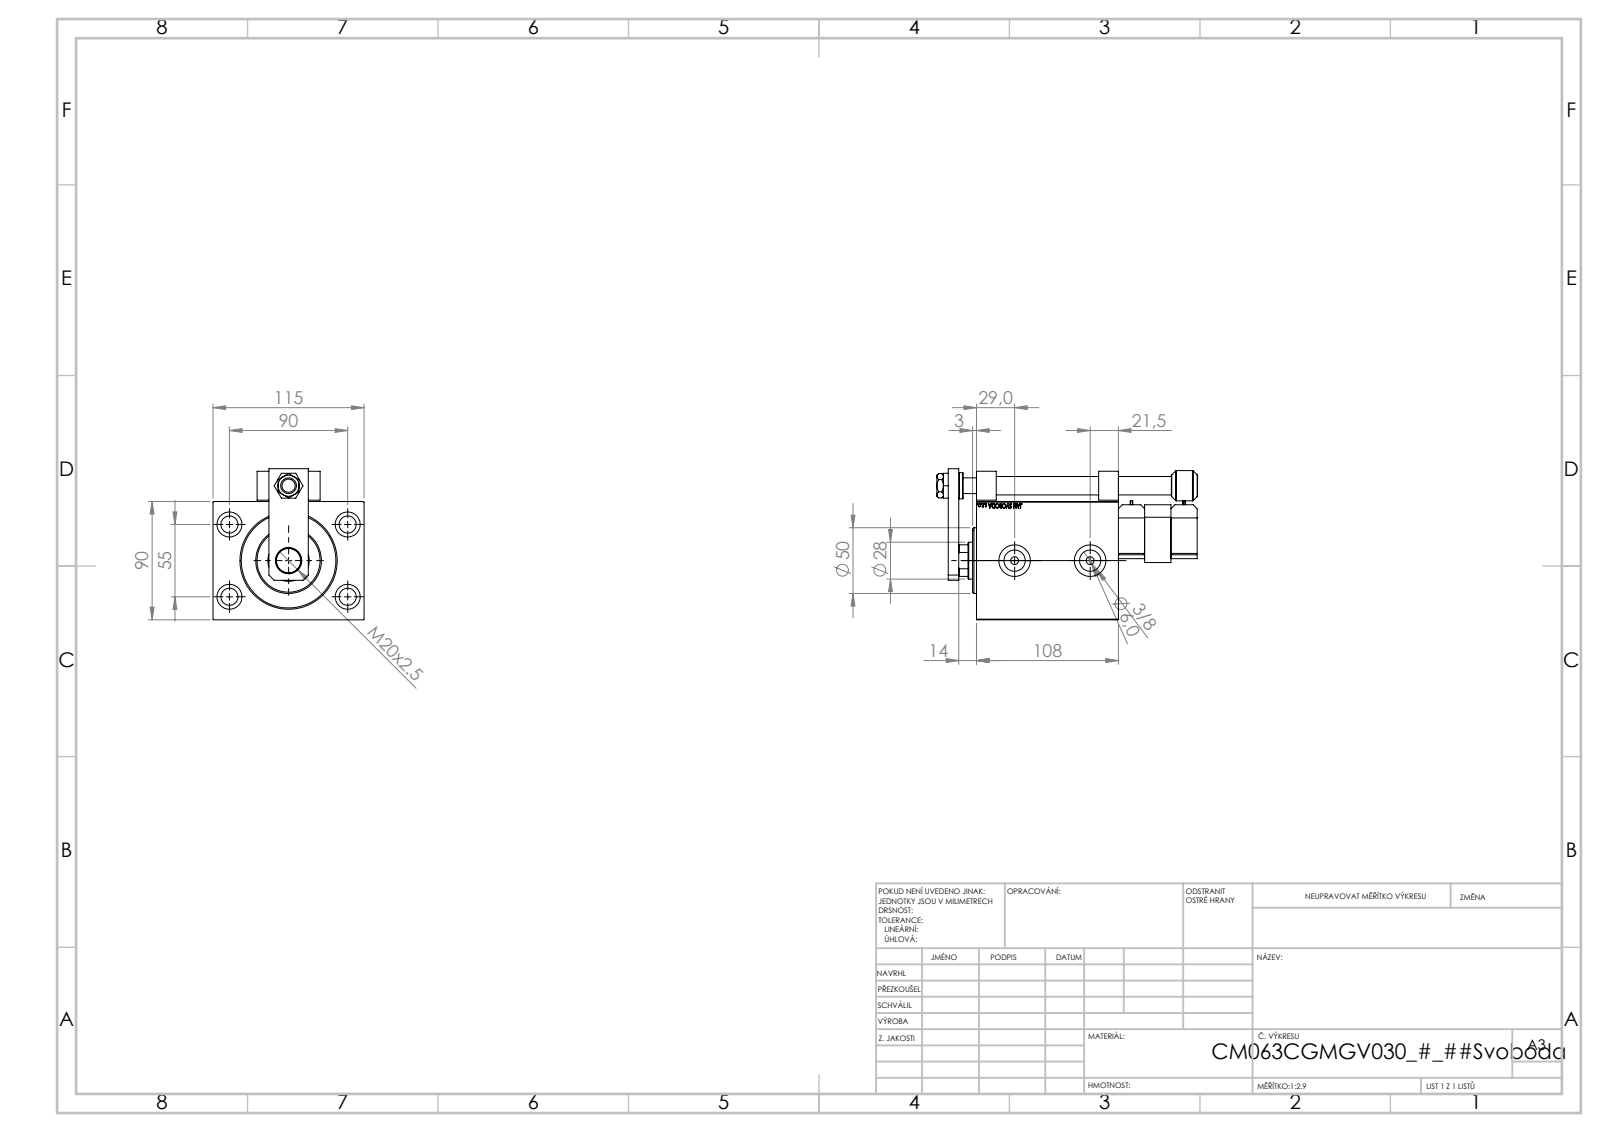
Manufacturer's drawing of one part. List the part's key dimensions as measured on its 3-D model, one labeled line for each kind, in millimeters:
Part name (STEP PRODUCT): MIDDLE; KROUZEK_PRO_TYC; V450CM_VC_B; SWITCH_P_FRONT_BACK (+7 more)
STEP written by: SolidWorks 2019 (CONFIG_CONTROL_DESIGN)
Units: millimetres
Bodies: 14 solids, 1090 faces (521 planar, 120 cylindrical, 449 other)
Overall size (bounding box): 198.5 × 115 × 115
Volume: 1 143 000 mm³ · Surface area: 187 436 mm²
Round holes (diameter × count): ⌀13 ×5, ⌀4 ×4, ⌀8 ×4, ⌀19 ×4, ⌀6 ×2, ⌀16.17 ×2, ⌀24 ×2, ⌀12 ×1, ⌀14 ×1, ⌀18.5 ×1, ⌀20 ×1, ⌀28 ×1
Round bosses / shafts (diameter × count): ⌀20 ×3, ⌀16 ×2, ⌀14 ×2, ⌀6 ×2, ⌀50 ×1, ⌀23 ×1
Partial cylindrical surfaces — rounded edges, fillets, slot ends (radius × count): R3 ×1, R13.5 ×1
Main face-to-face distances: 90, 115, 20, 108, 17.5, 37.5, 90.5, 40, 13.5, 77.5
Hole centre spacings: 52.74, 20, 53.81, 55, 90, 93, 95.13, 95.74
